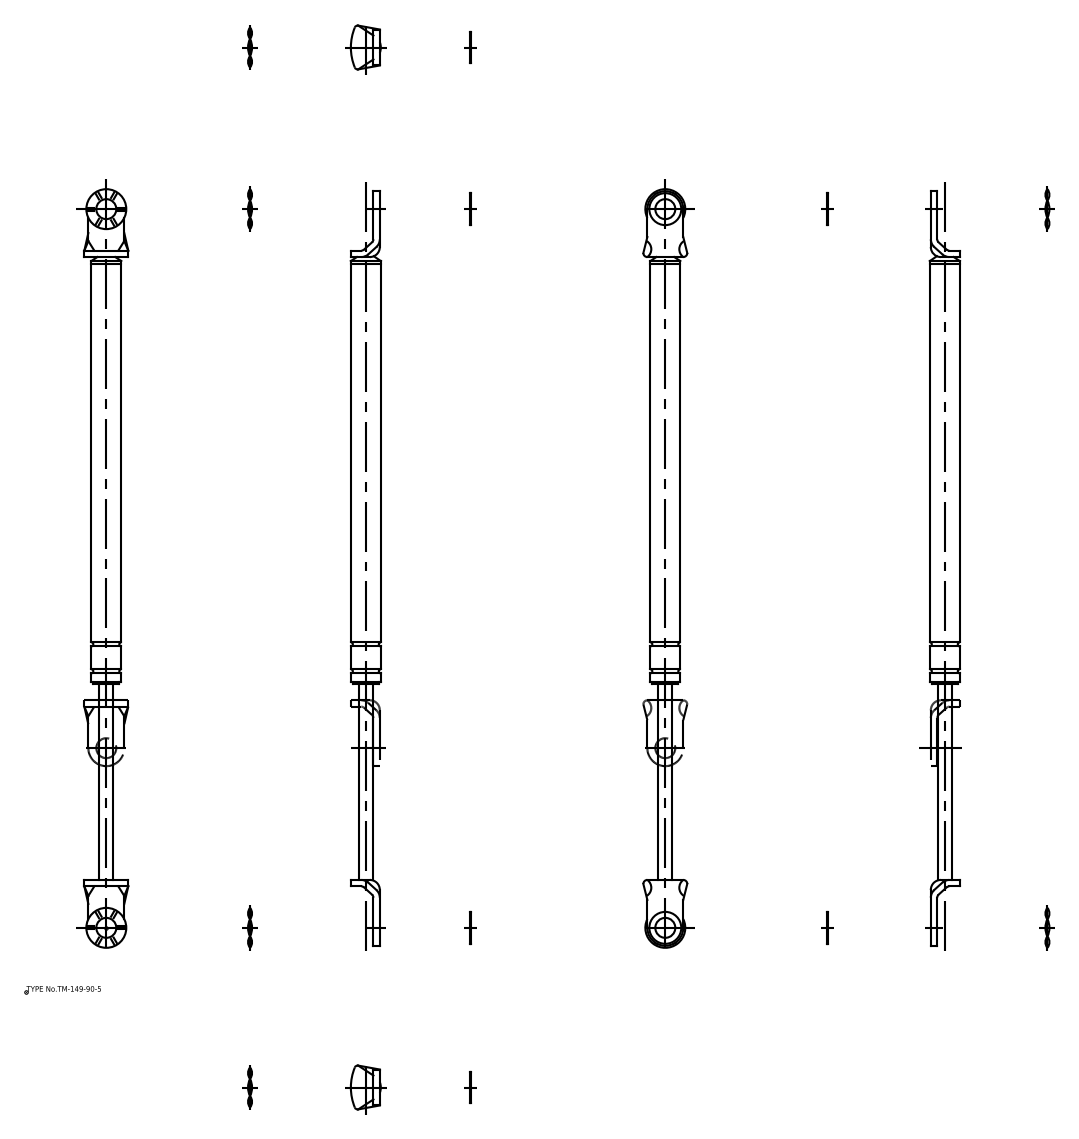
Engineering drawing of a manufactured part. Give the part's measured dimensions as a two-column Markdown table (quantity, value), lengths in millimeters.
| quantity | value |
| --- | --- |
| part name | washer_2; washer_1; body_div |
| STEP written by | spGate 16.7.1 (AUTOMOTIVE_DESIGN) |
| units | millimeters |
| bodies | 6 solids, 92 faces (44 planar, 42 cylindrical, 6 other) |
| overall size | 380 × 22 × 15.4 |
| volume | 46 883 mm³ |
| surface area | 18 118 mm² |
| round holes (diameter × count) | 10 × 2 |
| round bosses / shafts (diameter × count) | 20 × 2, 16 × 2, 15.4 × 1, 15 × 1, 13 × 1, 7 × 1 |
| partial cylindrical surfaces (radius × count) | 2 × 2, 5 × 2, 9 × 2, 17.12 × 1 |
| main face-to-face distances | 3.2, 2, 5.2, 315.2, 0.5, 3.7, 5.7, 318.4, 101.2, 217.2 |
| hole center spacings | 360 |
